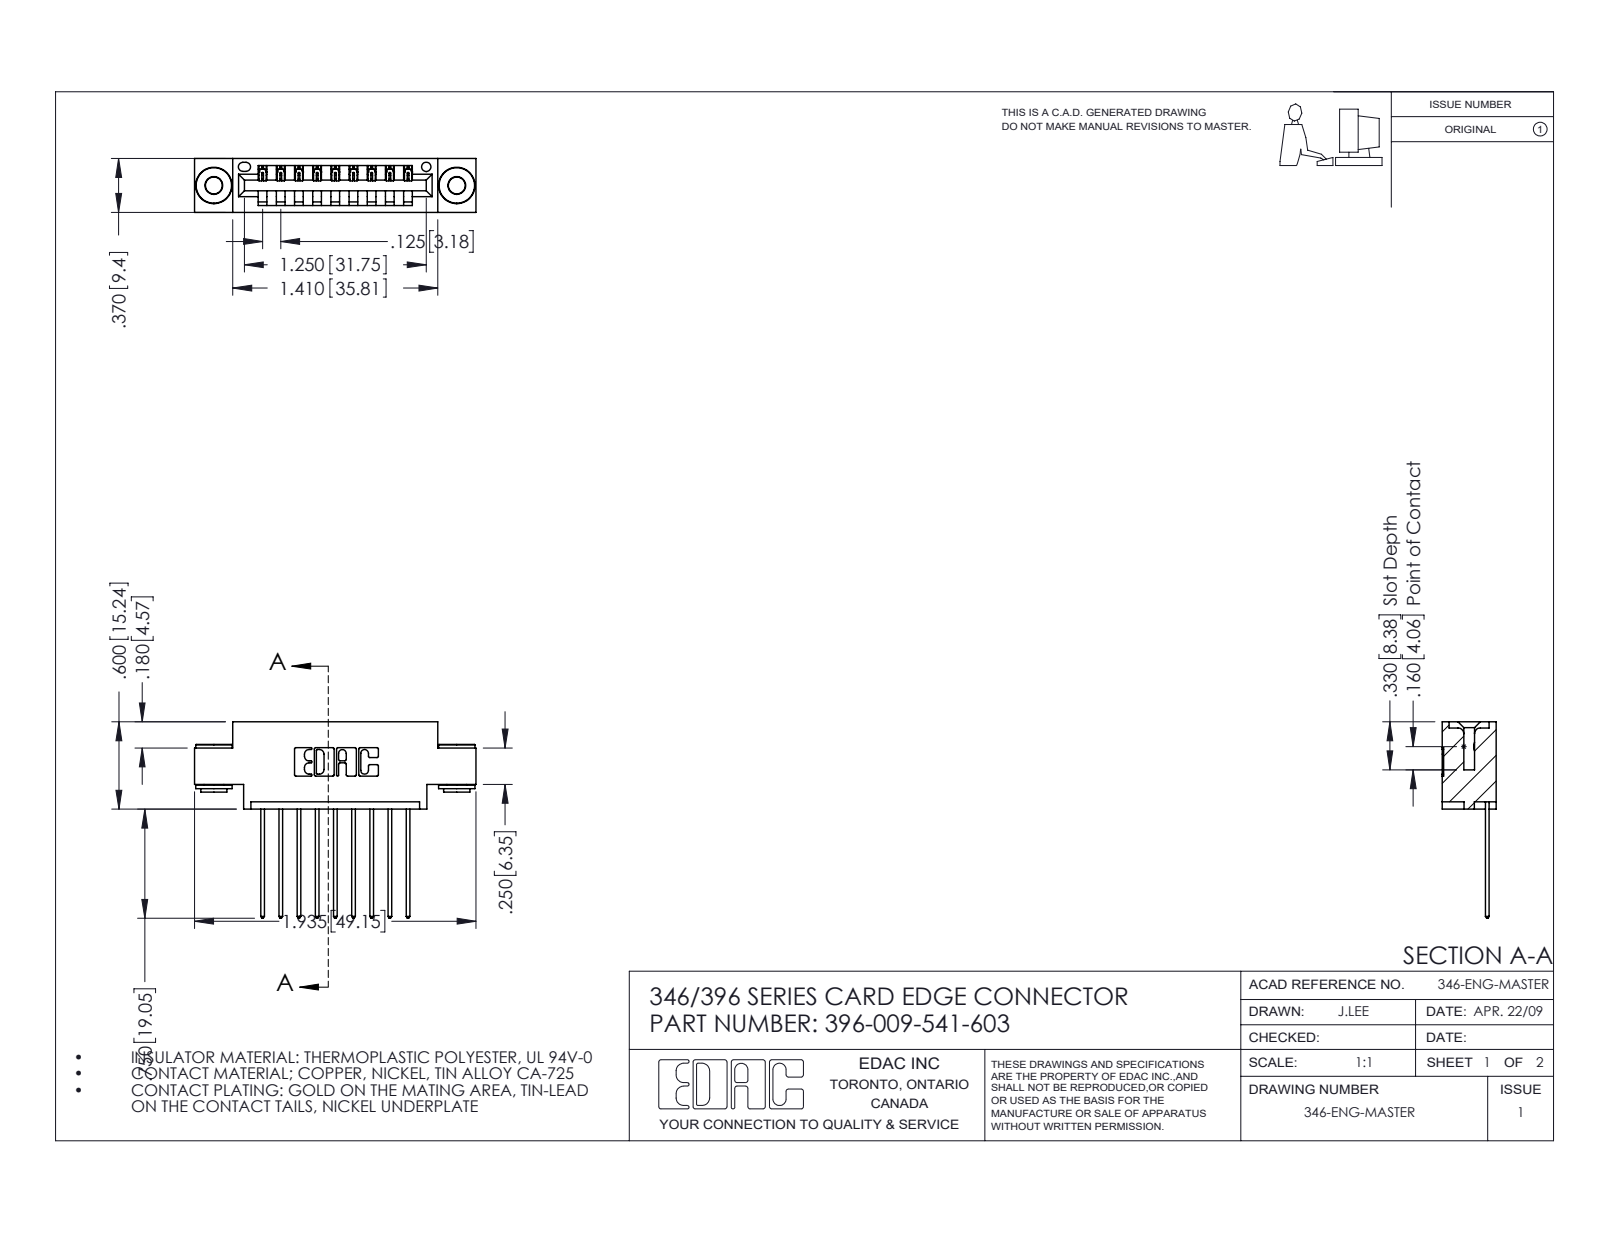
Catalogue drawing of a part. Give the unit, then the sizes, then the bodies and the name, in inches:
Units: inches
Overall size (bounding box): 1.935 × 1.35 × 0.37
Round holes (diameter × count): ⌀0.116 ×2, ⌀0.156 ×2, ⌀0.064 ×1
Round bosses / shafts (diameter × count): ⌀0.25 ×2, ⌀0.18 ×2, ⌀0.136 ×2
Partial cylindrical surfaces — rounded edges, fillets, slot ends (radius × count): R0.01 ×22, R0.006 ×18, R0.01 ×18, R0.007 ×6, R0.031 ×6, R0.026 ×3, R0.031 ×2, R0.04 ×2
Main face-to-face distances: 0.25, 0.37, 0.048, 0.322, 0.025, 0.072, 0.298, 0.148, 0.222, 0.1
Hole centre spacings: 0.246, 1.465, 1.67
Volume: 0.267 in³ · Surface area: 8.781 in²
Bodies: 12 solids, 686 faces (450 planar, 228 cylindrical, 8 other)
Part name (STEP PRODUCT): 396-009-541-603; 346 Part_0.170 Offset - 0.156 Dia-TH; 345-250-002_345-250-002-102; 345-292-001_345-293-141
STEP written by: SolidWorks 2016 (CONFIG_CONTROL_DESIGN)
